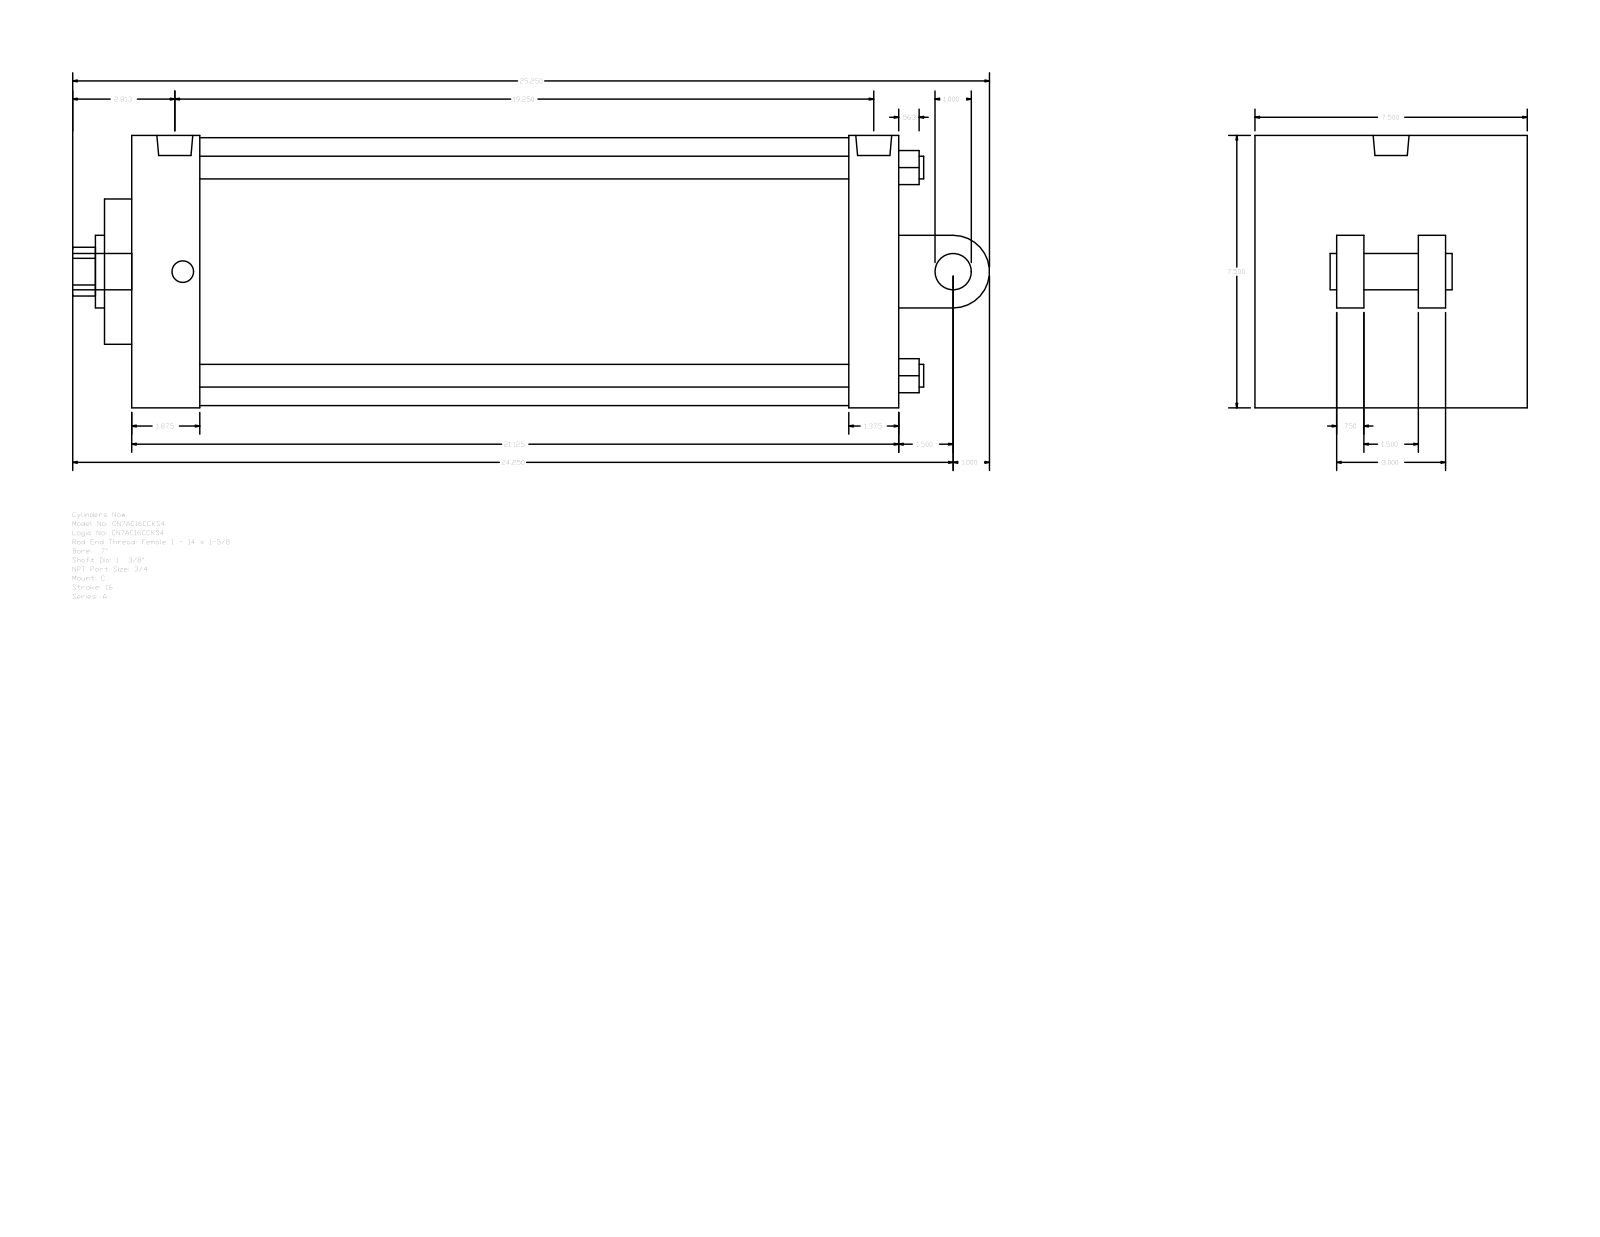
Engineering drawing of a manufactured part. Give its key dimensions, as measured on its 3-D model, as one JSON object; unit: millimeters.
{"part_name": "A_C__0700_1.375", "step_written_by": "GSSL Pune (CONFIG_CONTROL_DESIGN)", "units": "millimeters", "bodies": {"solids": 0, "faces": 104, "planar": 75, "cylindrical": 29, "other": 0}, "overall_size": [641.35, 190.5, 190.5], "round_holes": [[15.88, 4], [15.08, 2], [25.12, 1], [34.92, 1], [50.8, 1], [187.32, 1]], "round_bosses_or_shafts": [[25.4, 2], [15.08, 2], [25.12, 1]], "partial_cylinders_radius": [[17.06, 1], [25.4, 1]], "face_to_face_distances": [190.5, 536.58, 76.2, 57.15, 19.04, 555.62, 66.67, 47.63, 488.95, 520.69], "hole_center_spacings": [102.91, 145.54, 205.82, 5.56]}
